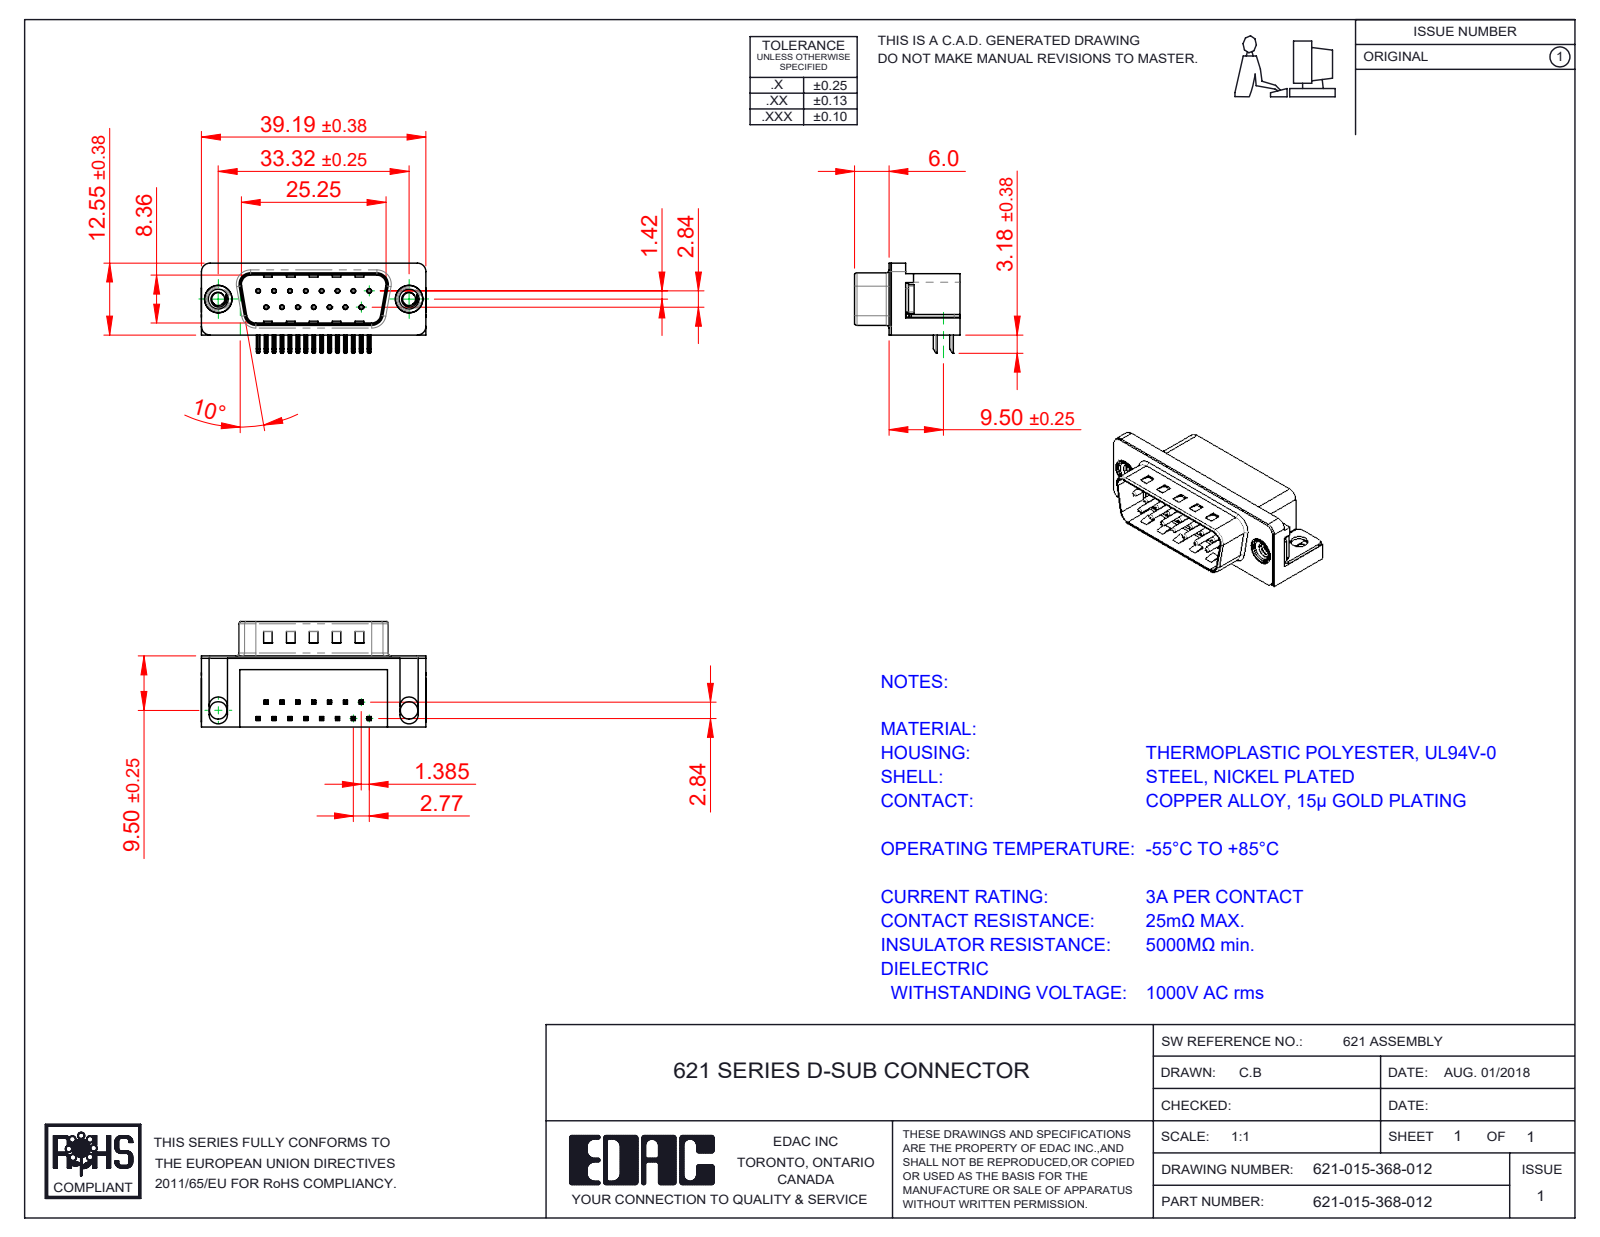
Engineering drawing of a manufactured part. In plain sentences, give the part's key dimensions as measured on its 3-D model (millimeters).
The part is named "621 Shell_15 Socket; 621 Thru Hole Board Mount; 621 4-40 Threaded Rivet; 621-015-368-012 (+3 more)". Its 3-D file was written by "SolidWorks 2016 (CONFIG_CONTROL_DESIGN)". It is 21 solids with 1475 faces: 891 planar, 445 cylindrical and 139 other. Overall it measures 39.22 by 18.4 by 15.73 millimeters. Its volume is 4 414 cubic millimeters and its surface area 5 637 square millimeters. Round holes: 15 of diameter 0.35, 15 of diameter 0.8, 2 of diameter 2.26, 2 of diameter 3.05, 2 of diameter 4, 2 of diameter 4.8, 2 of diameter 5. Round bosses or shafts: 15 of diameter 0.75, 2 of diameter 4.9, 2 of diameter 4.75, 2 of diameter 3.9. Partial cylindrical surfaces (rounded edges, fillets, slot ends): 68 of radius 0.25, 30 of radius 0.12, 16 of radius 1, 9 of radius 0.5, 8 of radius 1.6, 6 of radius 1.5, 4 of radius 0.9, 4 of radius 2. The main face-to-face distances are 0.4, 12, 10.35, 2.1, 10.46, 12.4, 1.7, 10.86, 8.76, 2.9. The hole center spacings are 3.16, 2.77, 5.54, 8.31, 11.08, 5.03, 5.04, 7.48.
